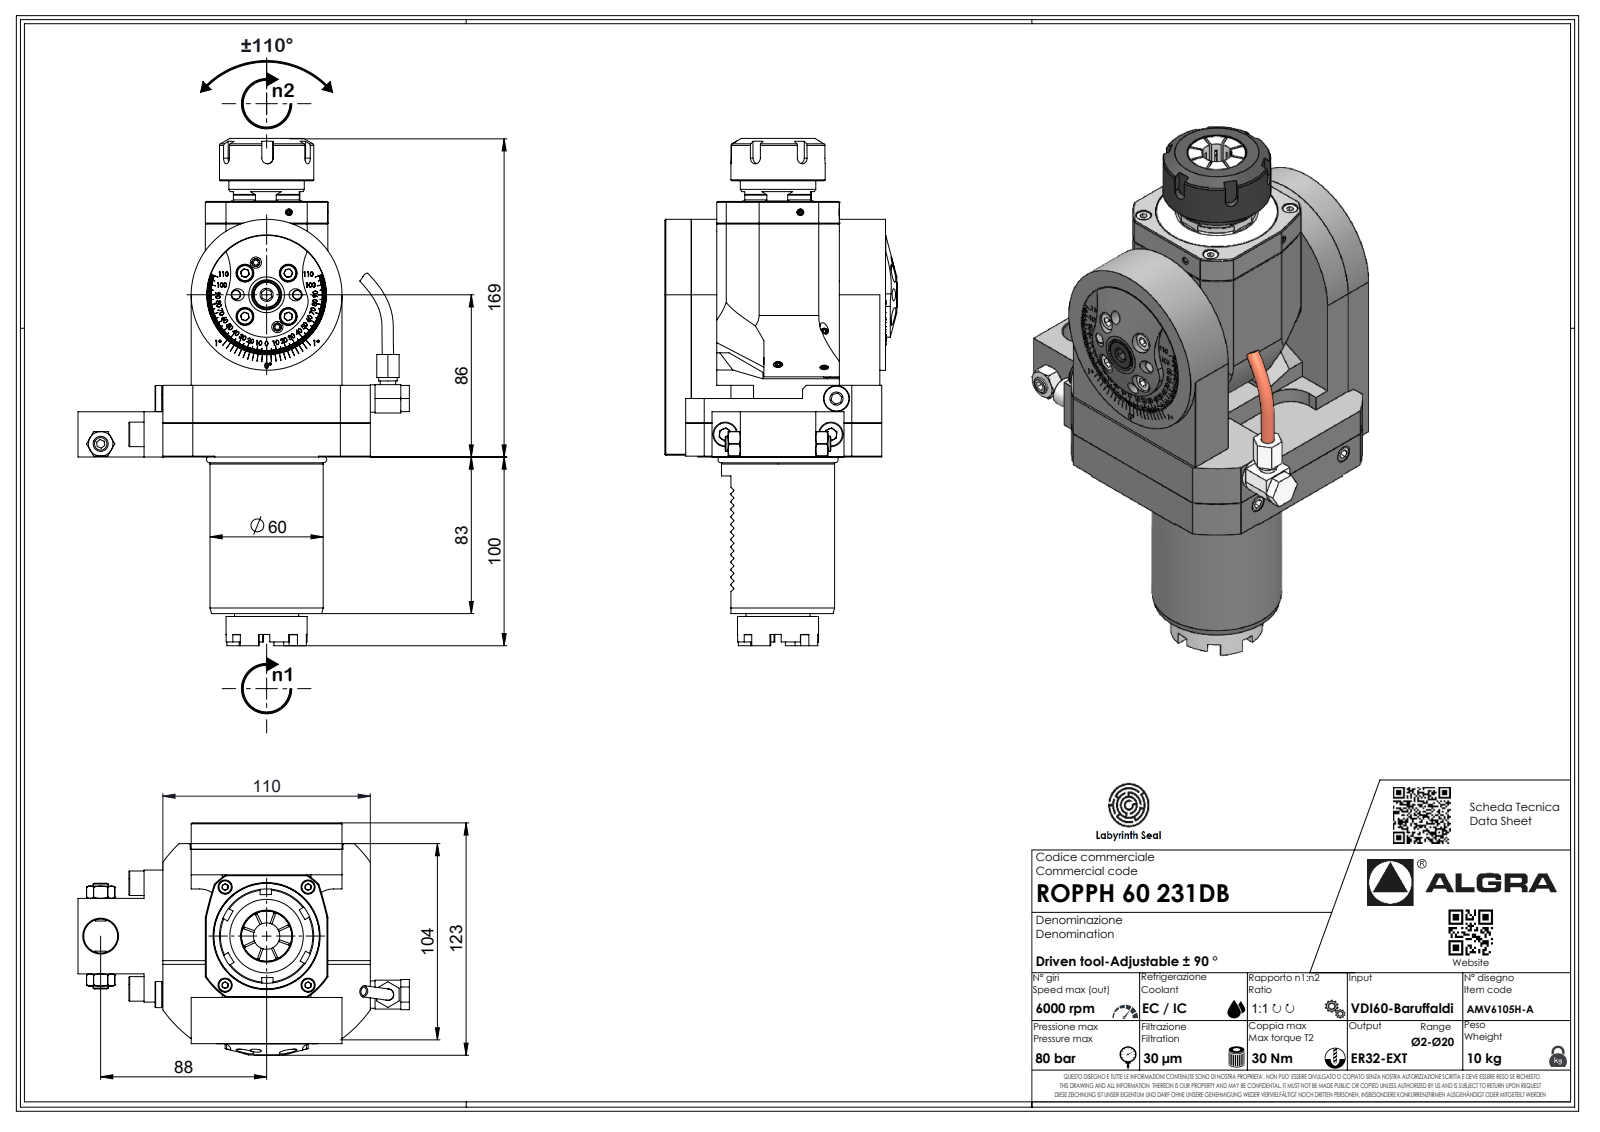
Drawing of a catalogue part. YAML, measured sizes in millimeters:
part_name: "ROPPH60231DB"
step_written_by: "SolidWorks 2023 (AUTOMOTIVE_DESIGN)"
units: millimeters
bodies: {solids: 1, faces: 666, planar: 431, cylindrical: 115, other: 120}
overall_size: [268.91, 175.7, 123]
volume: 1468000
surface_area: 125873
round_holes:
  - {diameter: 2.1, count: 1}
round_bosses_or_shafts:
  - {diameter: 80, count: 1}
  - {diameter: 60, count: 1}
  - {diameter: 58.7, count: 1}
  - {diameter: 50, count: 1}
  - {diameter: 43, count: 1}
  - {diameter: 40, count: 1}
  - {diameter: 34, count: 1}
  - {diameter: 14.5, count: 1}
partial_cylinders:
  - {radius: 0.2, count: 19}
  - {radius: 0.3, count: 14}
  - {radius: 0.33, count: 7}
  - {radius: 0.52, count: 7}
  - {radius: 3.7, count: 7}
  - {radius: 3, count: 5}
  - {radius: 10, count: 2}
  - {radius: 12, count: 2}
face_to_face_distances: [22.5, 87.5, 65, 80, 7.5, 95, 7, 15, 27.5, 72.5]
